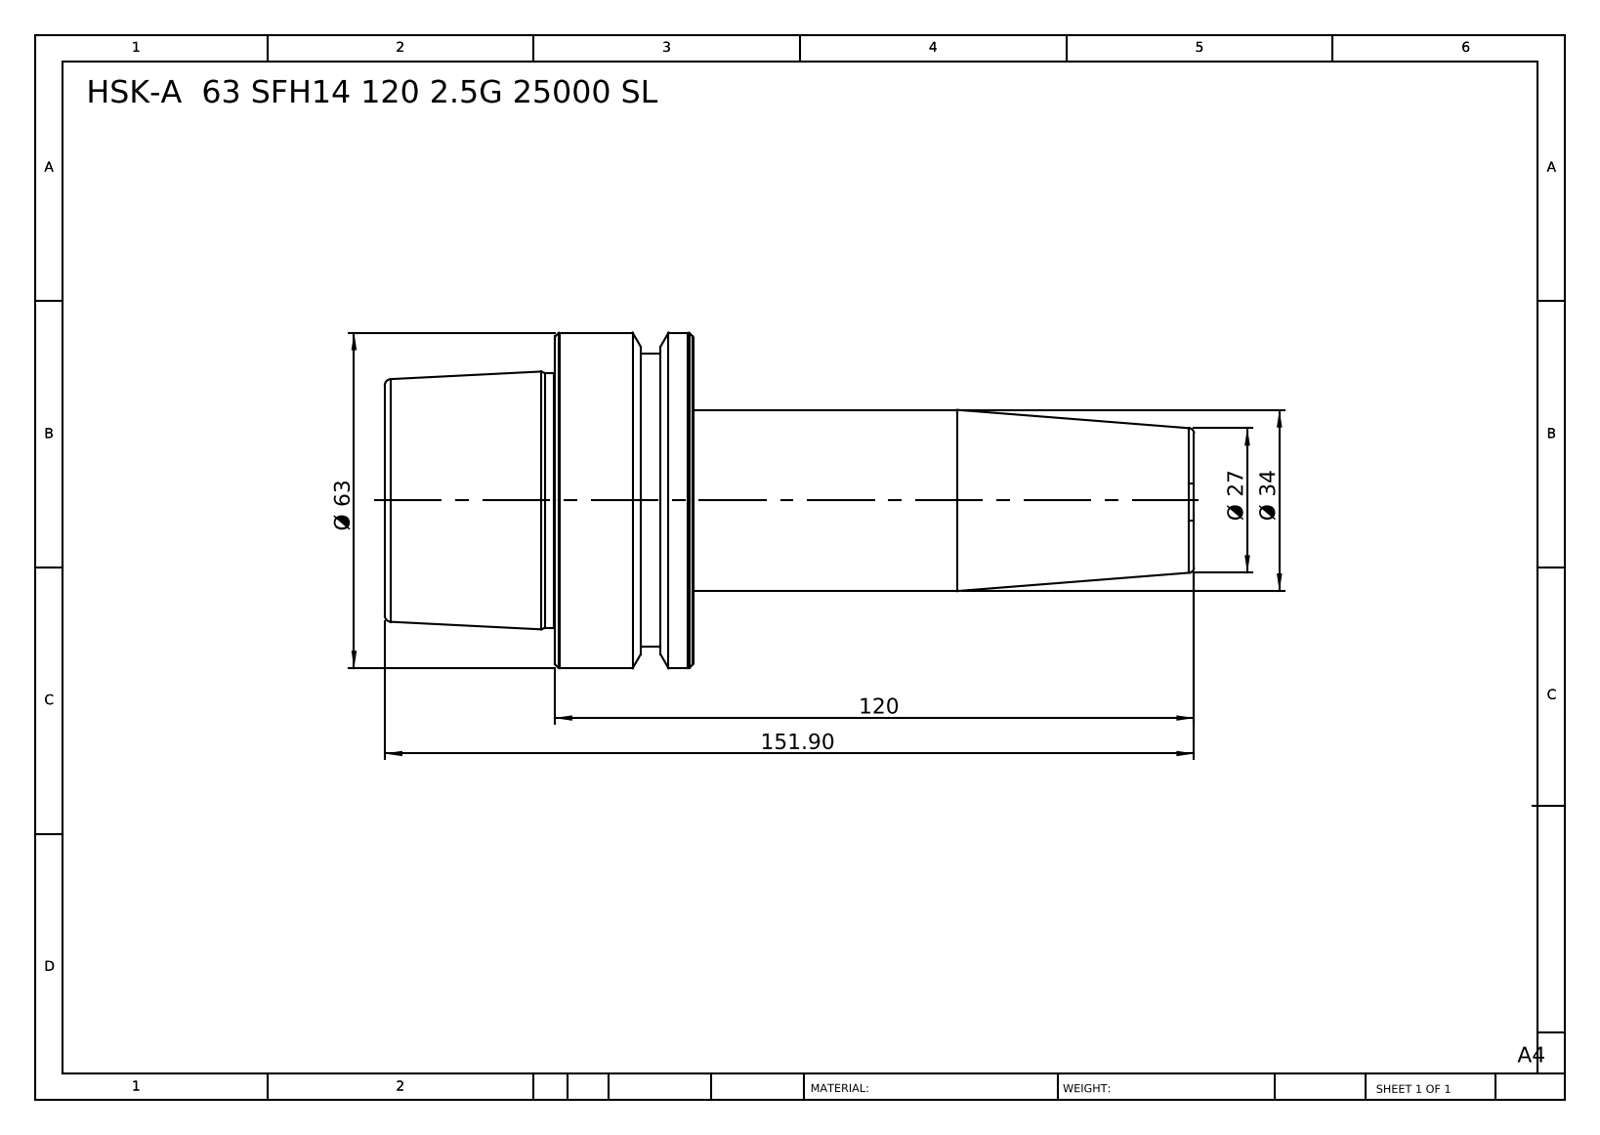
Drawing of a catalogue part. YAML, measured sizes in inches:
part_name: "HSK-A 63 SFH14 120 2.5G 25000 SL"
step_written_by: "SolidWorks 2014 (CONFIG_CONTROL_DESIGN)"
units: inches
bodies: {solids: 1, faces: 46, planar: 6, cylindrical: 10, other: 30}
overall_size: [5.98, 2.48, 2.48]
volume: 12.83
surface_area: 40.06
round_bosses_or_shafts:
  - {diameter: 2.48, count: 1}
  - {diameter: 2.165, count: 1}
  - {diameter: 1.881, count: 1}
  - {diameter: 1.339, count: 1}
face_to_face_distances: [2.28, 1.024, 1.256, 3.701, 4.724, 5.98, 3.941, 0.24, 0.783, 2.039]
